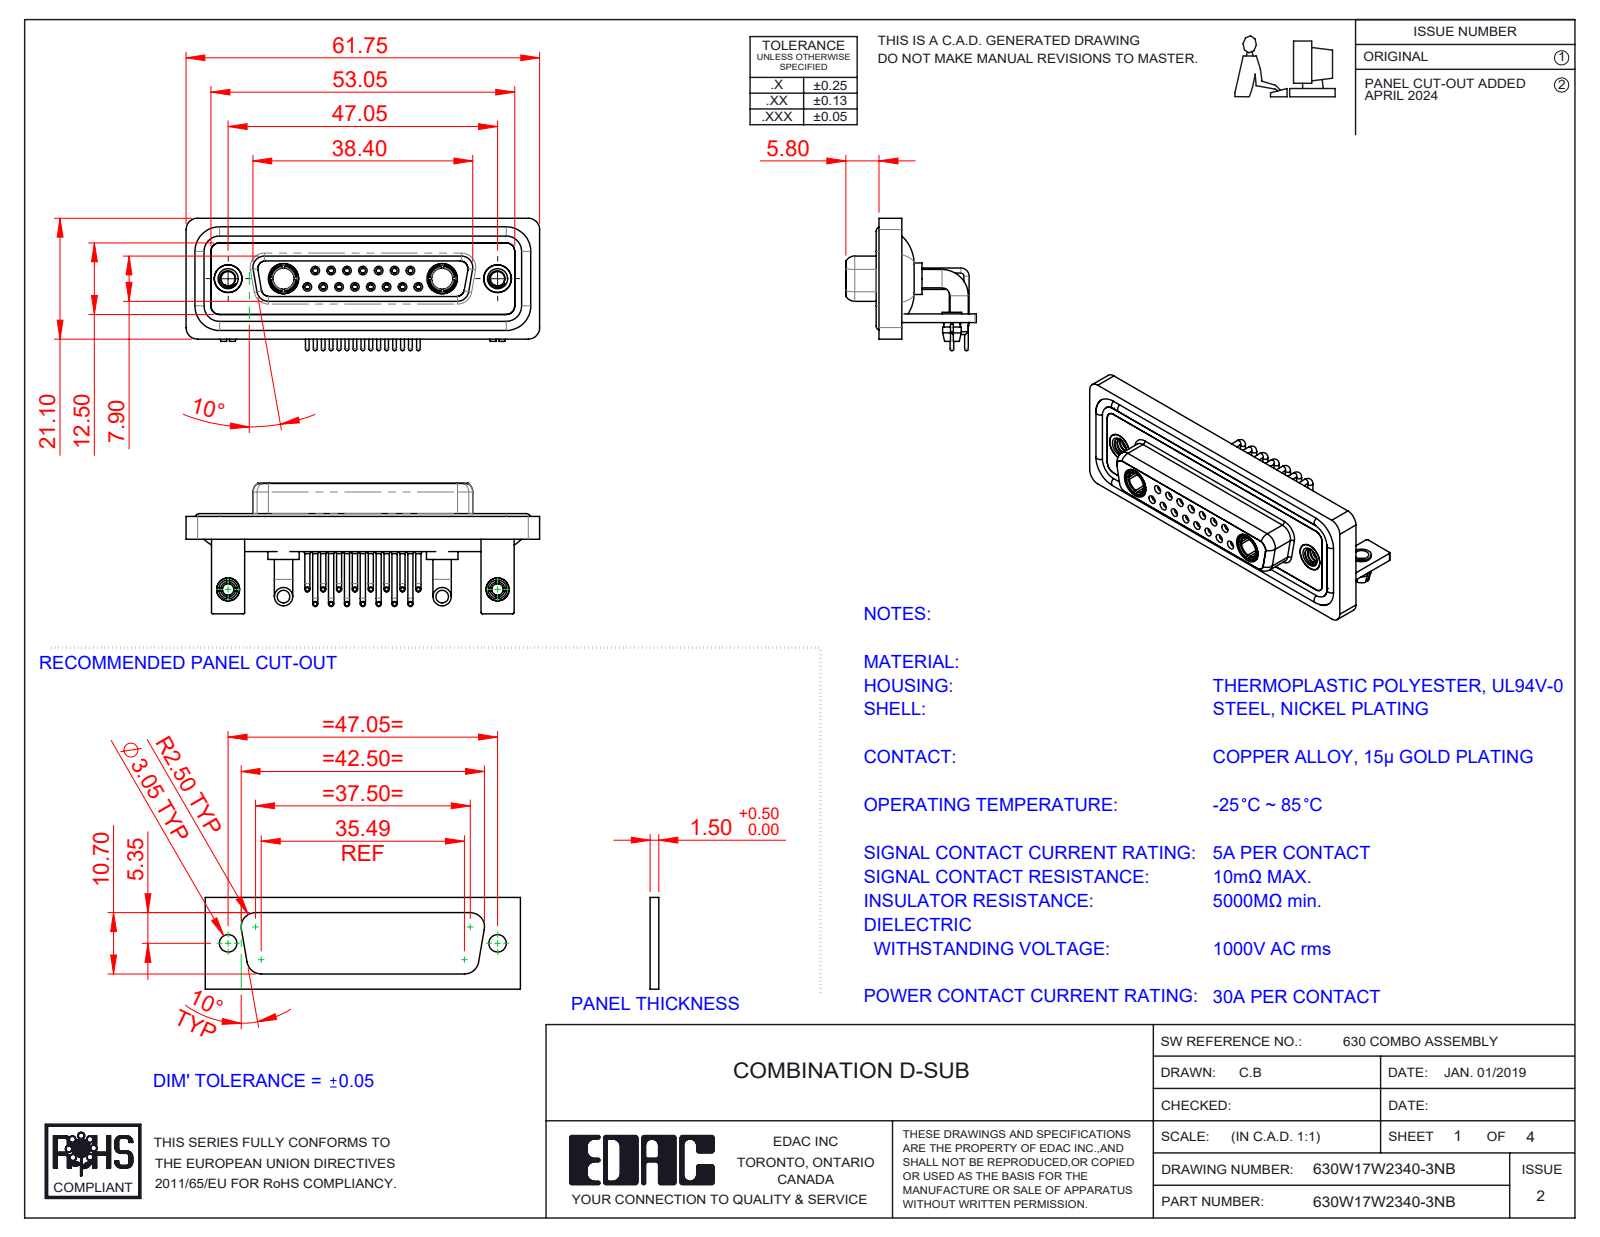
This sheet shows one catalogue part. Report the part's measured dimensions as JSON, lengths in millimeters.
{"part_name": "630Combo Stabilizer Bracket_50 Contacts; 630Combo Threaded Rivet_A; 630W17W2340-3NB; 630Combo Shell Rear_25 Contacts (+7 more)", "step_written_by": "SolidWorks 2023 (CONFIG_CONTROL_DESIGN)", "units": "millimeters", "bodies": {"solids": 30, "faces": 1471, "planar": 456, "cylindrical": 637, "other": 378}, "overall_size": [61.75, 23.12, 22.8], "volume_mm3": 8938, "surface_area_mm2": 15516, "round_holes": [[2, 17], [0.9, 15], [1.1, 15], [1.5, 15], [1.6, 8], [1.7, 7], [2.5, 4], [4.85, 4], [3.2, 2], [3.7, 2], [4, 2], [4.05, 2]], "round_bosses_or_shafts": [[0.9, 15], [0.65, 15], [1.6, 11], [3.2, 4], [5.5, 2], [5.2, 2], [4.96, 2], [4.95, 2]], "partial_cylinders_radius": [[2, 19], [1.5, 18], [0.25, 16], [1.35, 8], [1.6, 8], [0.5, 5], [0.6, 4], [0.65, 4]], "face_to_face_distances": [0.4, 1.8, 2.9, 3.7, 1.5, 4.1, 1.1, 1.4, 1.6, 3.1], "hole_center_spacings": [3.16, 2.77, 5.54, 8.31, 5.04, 7.49, 11.08, 5.03]}
